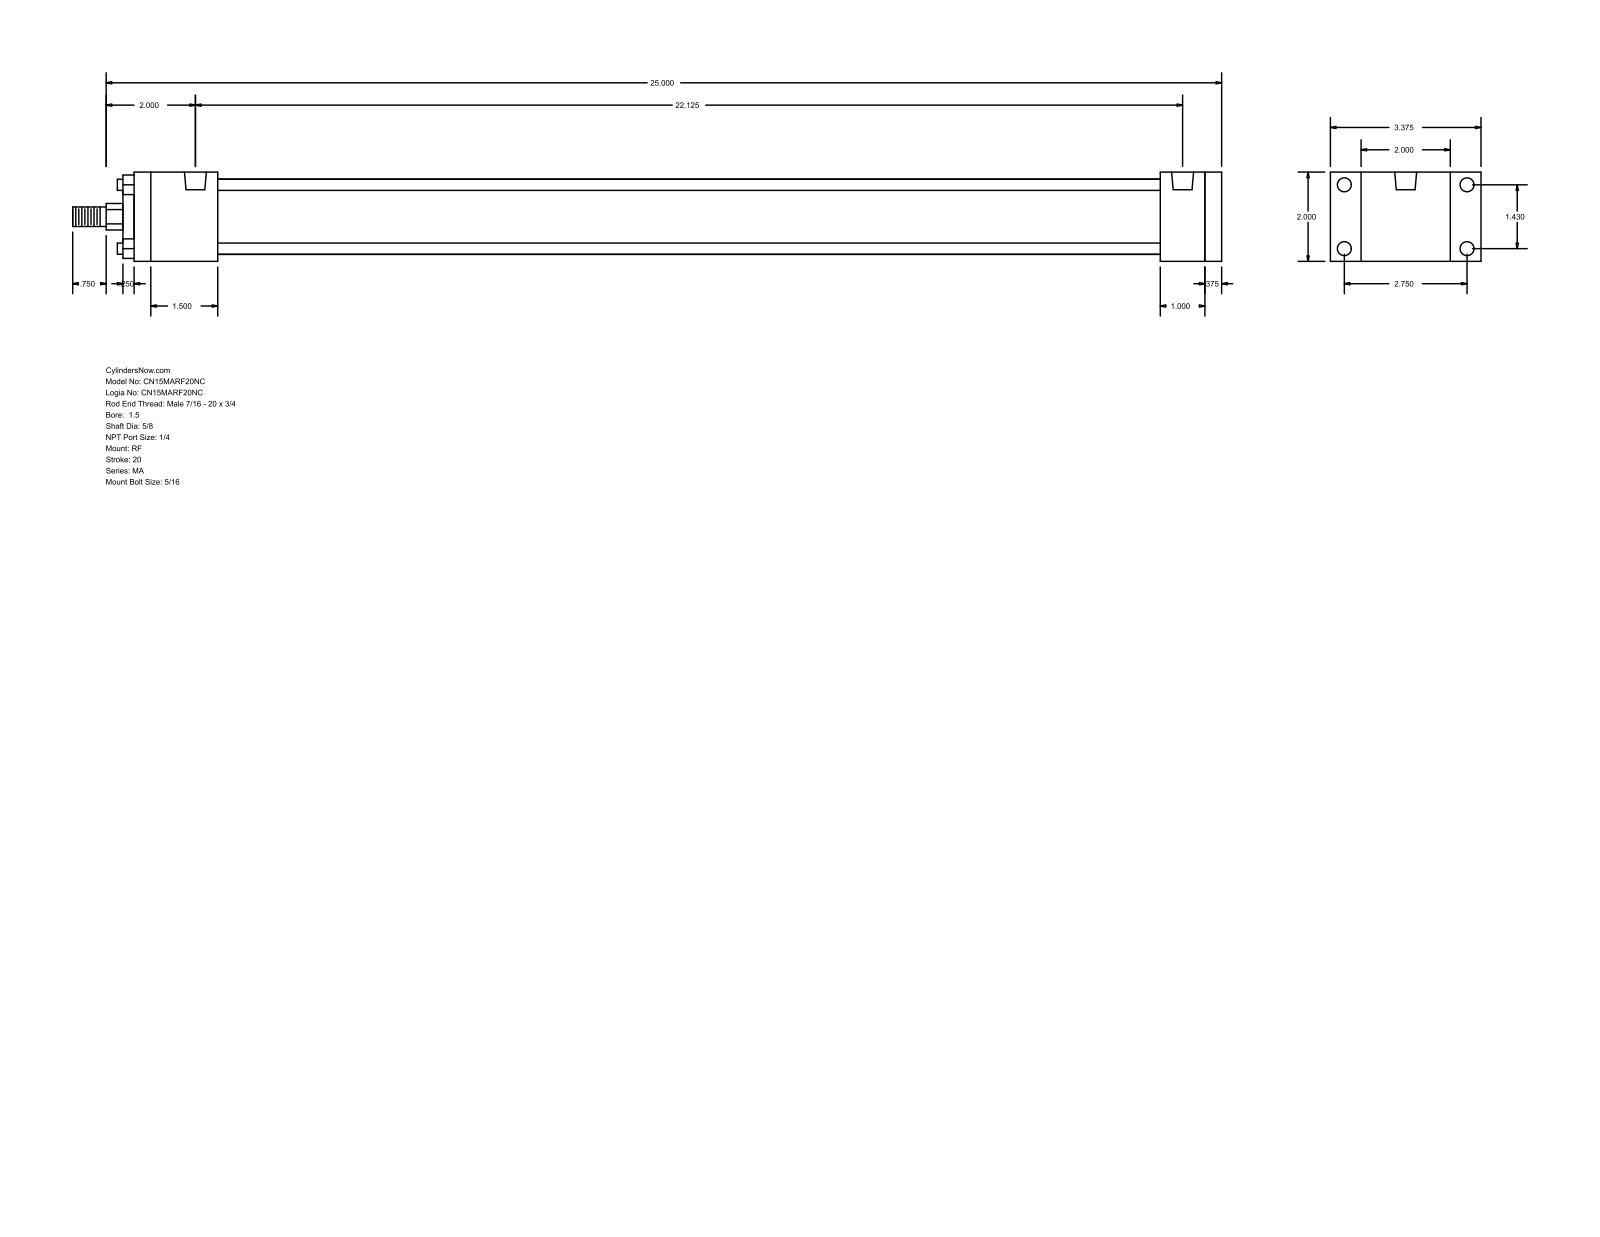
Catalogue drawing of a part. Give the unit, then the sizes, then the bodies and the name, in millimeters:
Units: millimetres
Overall size (bounding box): 654.05 × 85.72 × 50.8
Round holes (diameter × count): ⌀7.94 ×8, ⌀12.49 ×2
Round bosses / shafts (diameter × count): ⌀6.35 ×4, ⌀42.93 ×1, ⌀28.57 ×1, ⌀15.88 ×1, ⌀11.11 ×1
Partial cylindrical surfaces — rounded edges, fillets, slot ends (radius × count): R7.54 ×1
Main face-to-face distances: 50.8, 9.52, 609.6, 619.12, 25.4, 584.2, 34.92, 47.62, 536.58, 561.98
Hole centre spacings: 36.32, 69.84, 78.72, 561.97
Bodies: 0 solids, 92 faces (64 planar, 28 cylindrical, 0 other)
Part name (STEP PRODUCT): MA_RF__0150_0.625
STEP written by: GSSL Pune (CONFIG_CONTROL_DESIGN)
